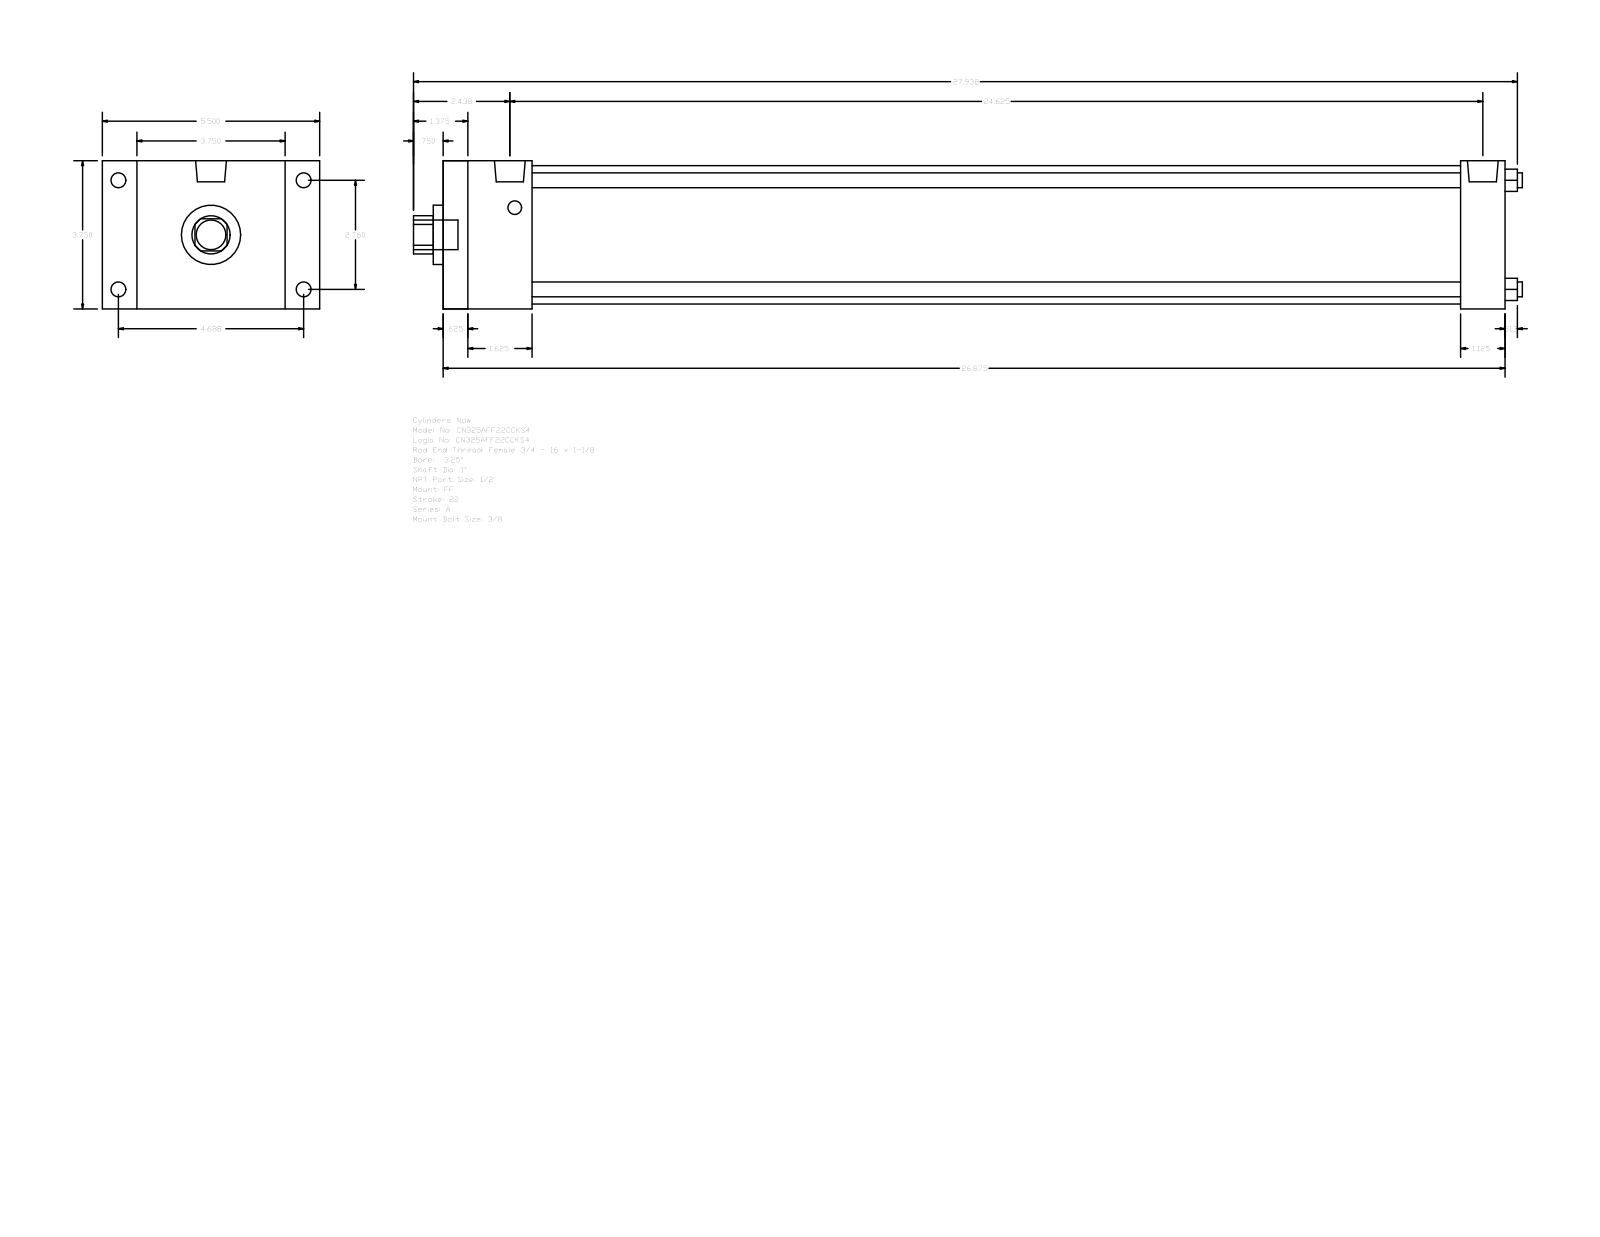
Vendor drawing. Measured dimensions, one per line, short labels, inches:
name: A_FF__0325_1
written by: GSSL Pune (CONFIG_CONTROL_DESIGN)
unit: in
bodies: 0 solids, 92 faces (64 planar, 28 cylindrical, 0 other)
size: 28.063 × 5.5 × 3.75
holes: 4× ⌀0.375, 1× ⌀1, 1× ⌀1.5, 1× ⌀3.5
bosses: 4× ⌀0.375, 4× ⌀0.344, 2× ⌀0.778, 1× ⌀0.75
rounds: 1× R0.484
face distances: 3.75, 26.875, 0.625, 26.25, 0.875, 4.625, 1.125, 2.25, 25.75, 1.625
hole spacings: 1.952, 2.76, 3.903
